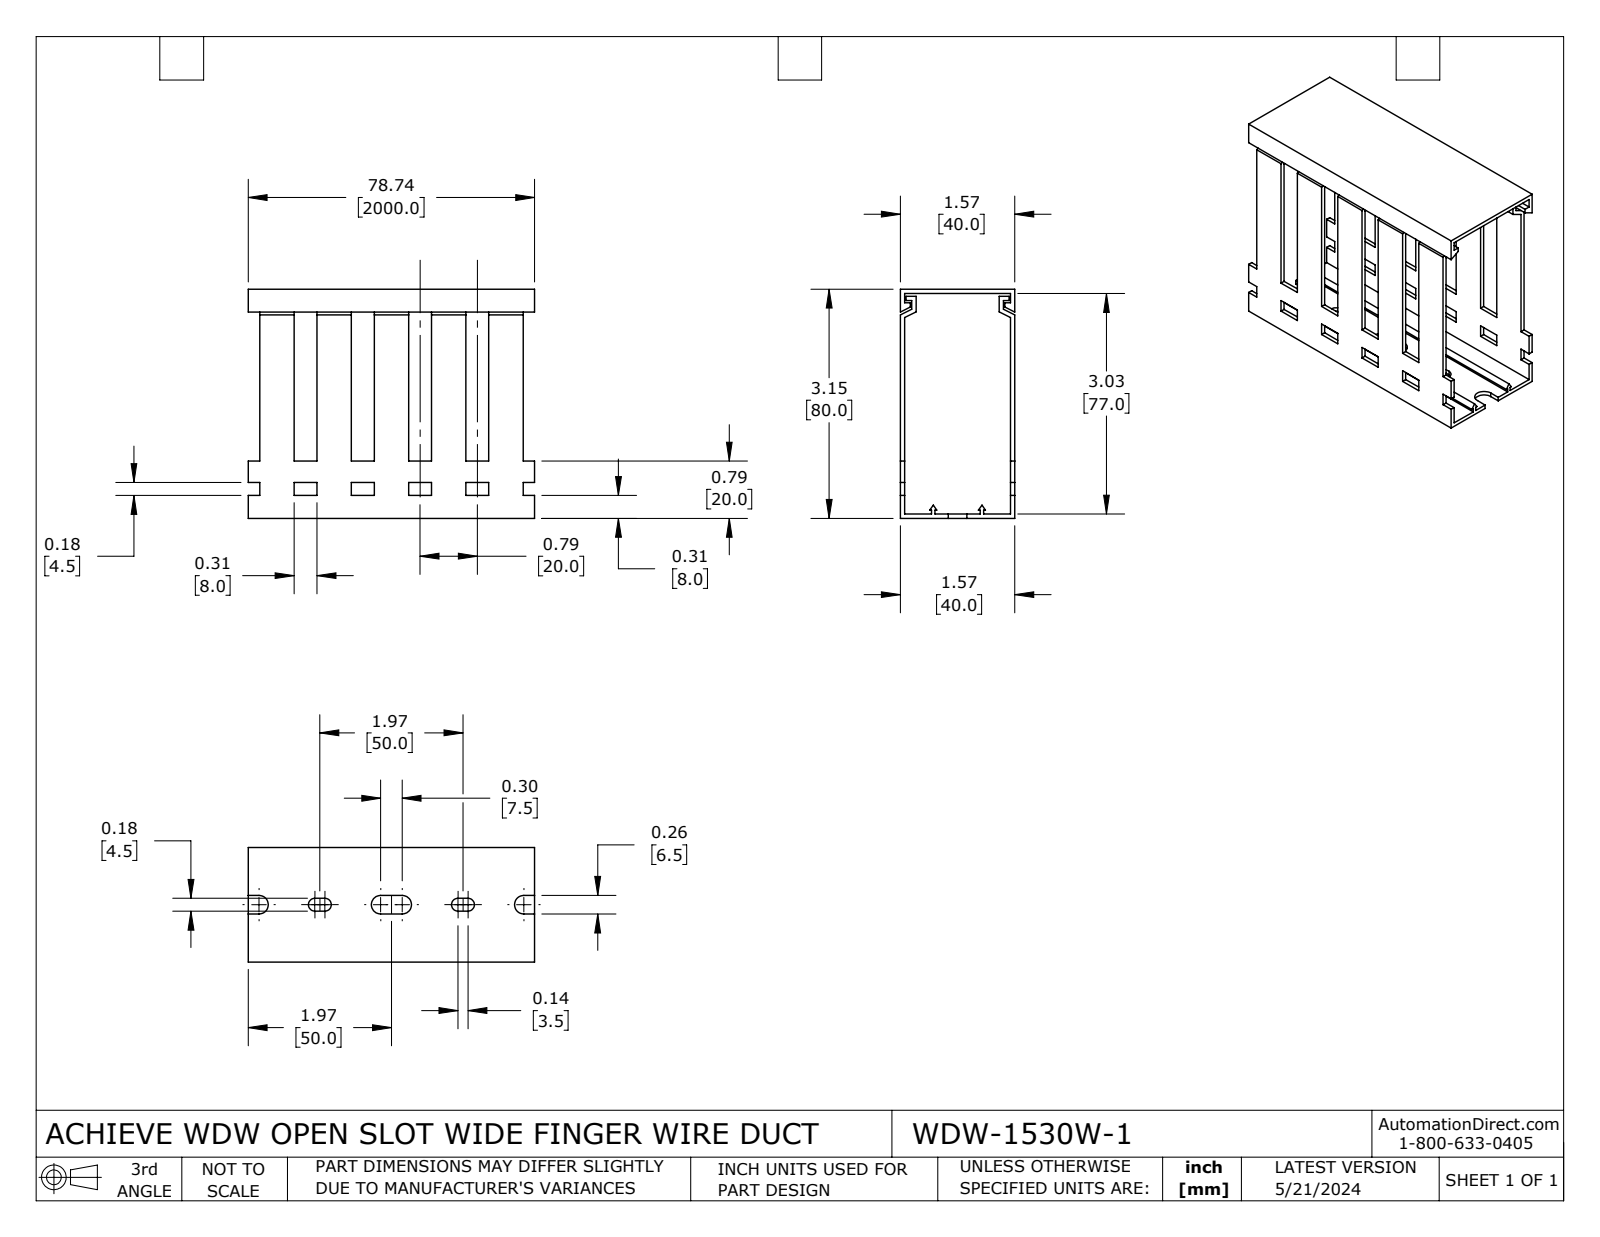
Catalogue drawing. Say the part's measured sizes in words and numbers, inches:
The part is named "WDW-1530W-1". Its 3-D file was written by "SolidWorks 2023 (CONFIG_CONTROL_DESIGN)". It is 2 solids with 210 faces: 198 planar, 12 cylindrical and 0 other. Overall it measures 3.937 by 3.15 by 1.575 inches. Its volume is 1.906 cubic inches and its surface area 69.81 square inches. Partial cylindrical surfaces (rounded edges, fillets, slot ends): 4 of radius 0.089, 4 of radius 0.128. The main face-to-face distances are 0.059, 1.516, 3.091, 1.575, 1.457, 3.15, 3.031, 0.787, 0.157, 1.358.
